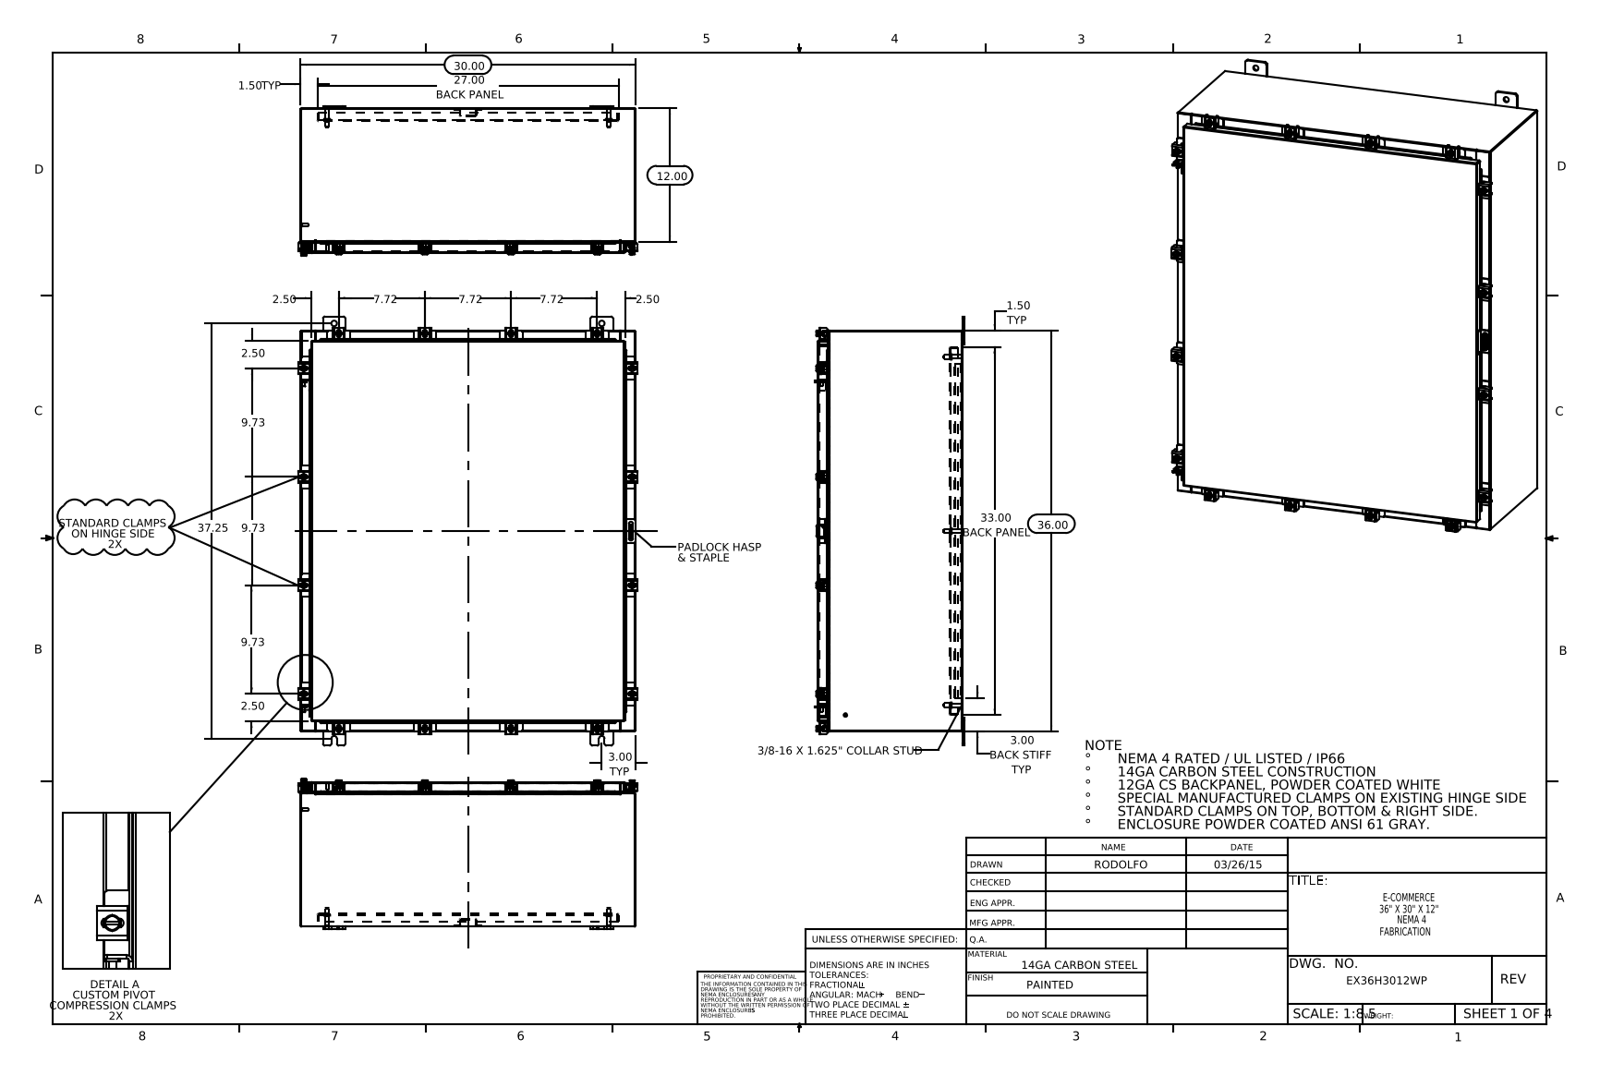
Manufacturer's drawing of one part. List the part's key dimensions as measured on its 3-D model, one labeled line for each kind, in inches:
Part name (STEP PRODUCT): EX36H3012WP Padlock Staple; HW-CLN-NH-20330; EX36H3012WP Backpanel; EX36H3012WP Body (+8 more)
STEP written by: SolidWorks 2014 (AUTOMOTIVE_DESIGN)
Units: inches
Bodies: 109 solids, 2711 faces (1431 planar, 1060 cylindrical, 220 other)
Overall size (bounding box): 38.5 × 30.421 × 13.453
Volume: 421.1 in³ · Surface area: 10 507 in²
Round holes (diameter × count): ⌀0.213 ×17, ⌀0.26 ×17, ⌀0.5 ×10, ⌀0.125 ×1, ⌀0.25 ×1
Round bosses / shafts (diameter × count): ⌀0.5 ×17, ⌀0.25 ×17, ⌀0.399 ×15, ⌀0.625 ×6, ⌀0.375 ×6, ⌀0.33 ×6, ⌀0.315 ×2, ⌀0.236 ×2
Partial cylindrical surfaces — rounded edges, fillets, slot ends (radius × count): R0.06 ×74, R0.141 ×34, R0.12 ×32, R0.013 ×30, R0.088 ×26, R0.09 ×24, R0.19 ×24, R0.05 ×23
Main face-to-face distances: 0.075, 12.9, 12.826, 12.975, 0.104, 1, 1.075, 11.826, 11.9, 1.179
Hole centre spacings: 31.017, 35.451, 2.347, 4.44, 5.299, 9.73, 10.964, 13.241
